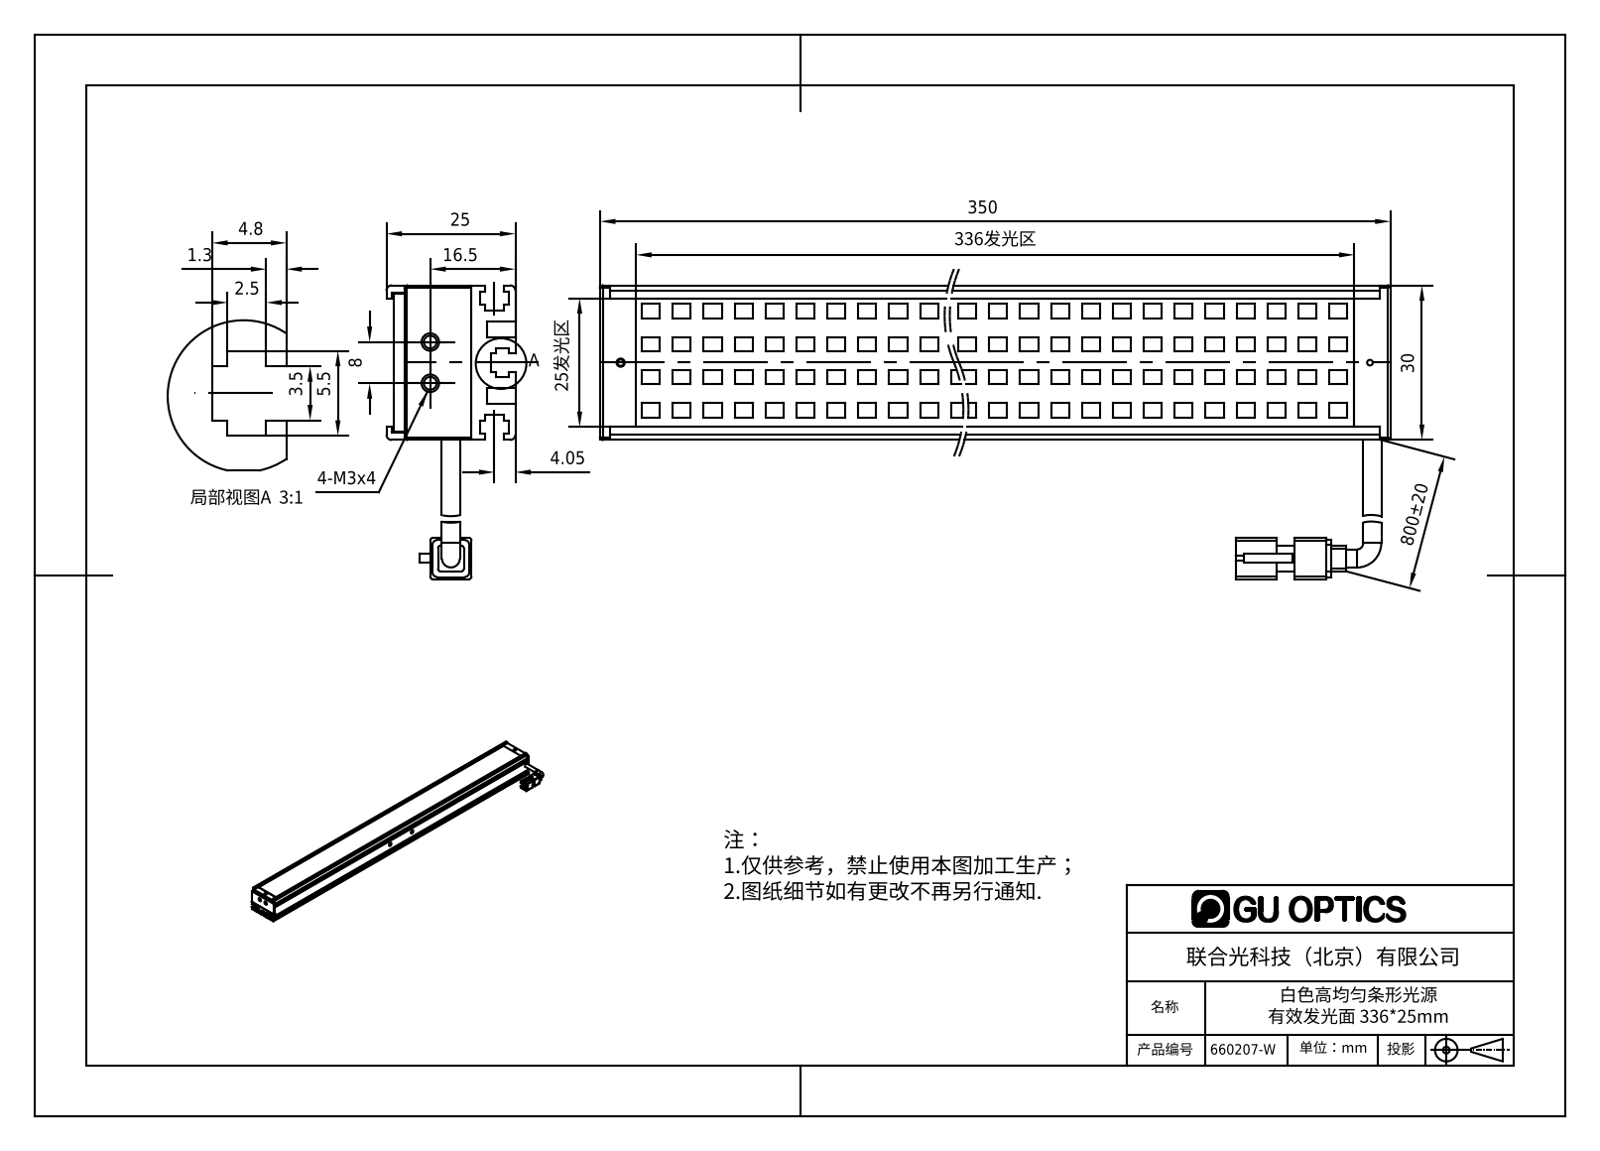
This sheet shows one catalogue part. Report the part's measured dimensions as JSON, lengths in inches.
{"part_name": "660207-W", "step_written_by": "SolidWorks 2016 (AUTOMOTIVE_DESIGN)", "units": "inches", "bodies": {"solids": 6, "faces": 1564, "planar": 1378, "cylindrical": 83, "other": 103}, "overall_size": [13.78, 2.244, 0.984], "volume_in3": 7.203, "surface_area_in2": 186.8, "round_holes": [[0.063, 5], [0.059, 2], [0.067, 2], [0.098, 2], [0.11, 2], [0.118, 2], [0.043, 1], [0.049, 1], [0.079, 1]], "round_bosses_or_shafts": [[0.138, 2]], "partial_cylinders_radius": [[0.039, 12], [0.02, 8], [0.065, 1]], "face_to_face_distances": [0.039, 0.512, 0.079, 0.098, 0.118, 1.083, 0.374, 0.177, 0.472, 0.594], "hole_center_spacings": [13.465, 0.276, 6.142, 6.147, 7.323, 7.328, 13.467, 0.315]}
